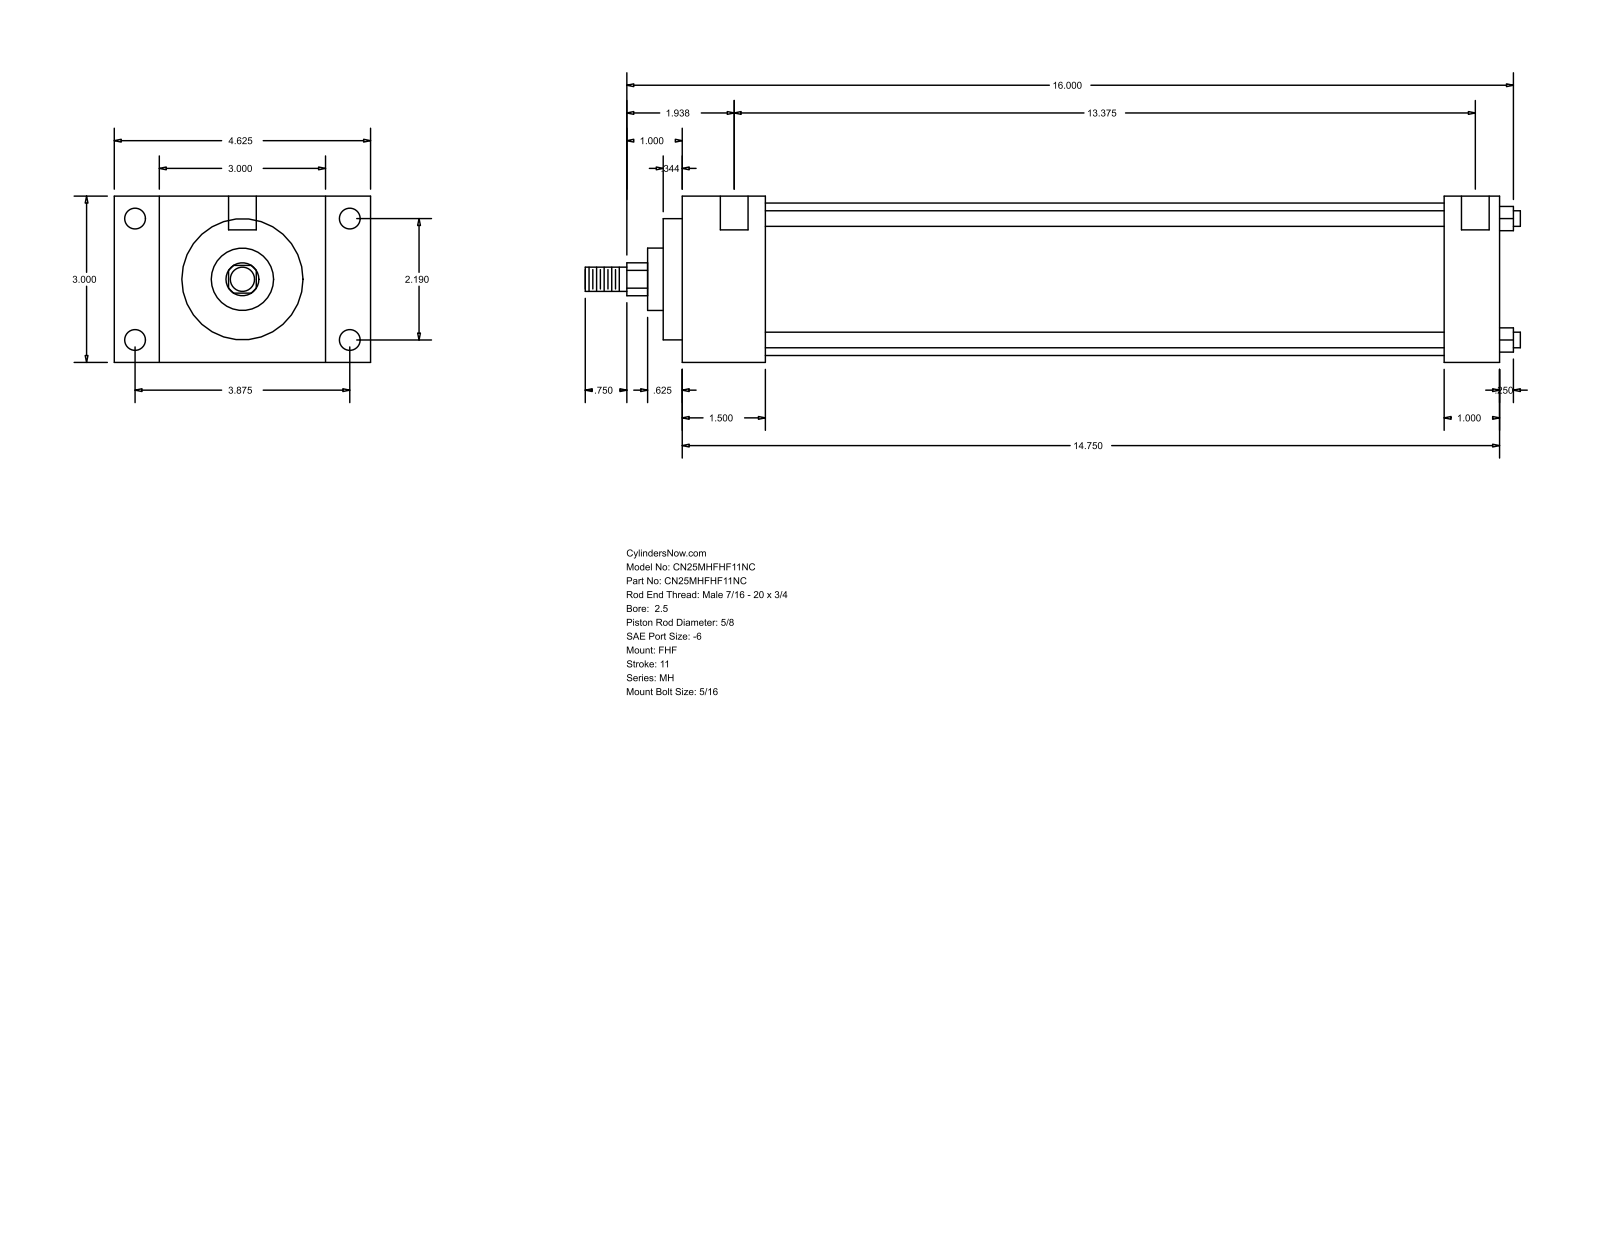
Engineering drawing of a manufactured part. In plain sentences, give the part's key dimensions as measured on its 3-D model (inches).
The part is named "MH_FHF__0250_0.625". Its 3-D file was written by "GSSL Pune (CONFIG_CONTROL_DESIGN)". It is 0 solids with 90 faces: 61 planar, 29 cylindrical and 0 other. Overall it measures 16.875 by 4.625 by 3 inches. Round holes: 4 of diameter 0.219, 4 of diameter 0.375, 2 of diameter 0.5. Round bosses or shafts: 4 of diameter 0.281, 1 of diameter 2.75, 1 of diameter 2.187, 1 of diameter 1.125, 1 of diameter 0.625, 1 of diameter 0.437. Partial cylindrical surfaces (rounded edges, fillets, slot ends): 1 of radius 0.297. The main face-to-face distances are 3, 14.75, 1.5, 13.25, 0.813, 3.813, 4.625, 1, 13.75, 12.25. The hole center spacings are 2.19, 3.875, 4.451, 13.687, 0.125, 0.187, 13.375, 13.5.
